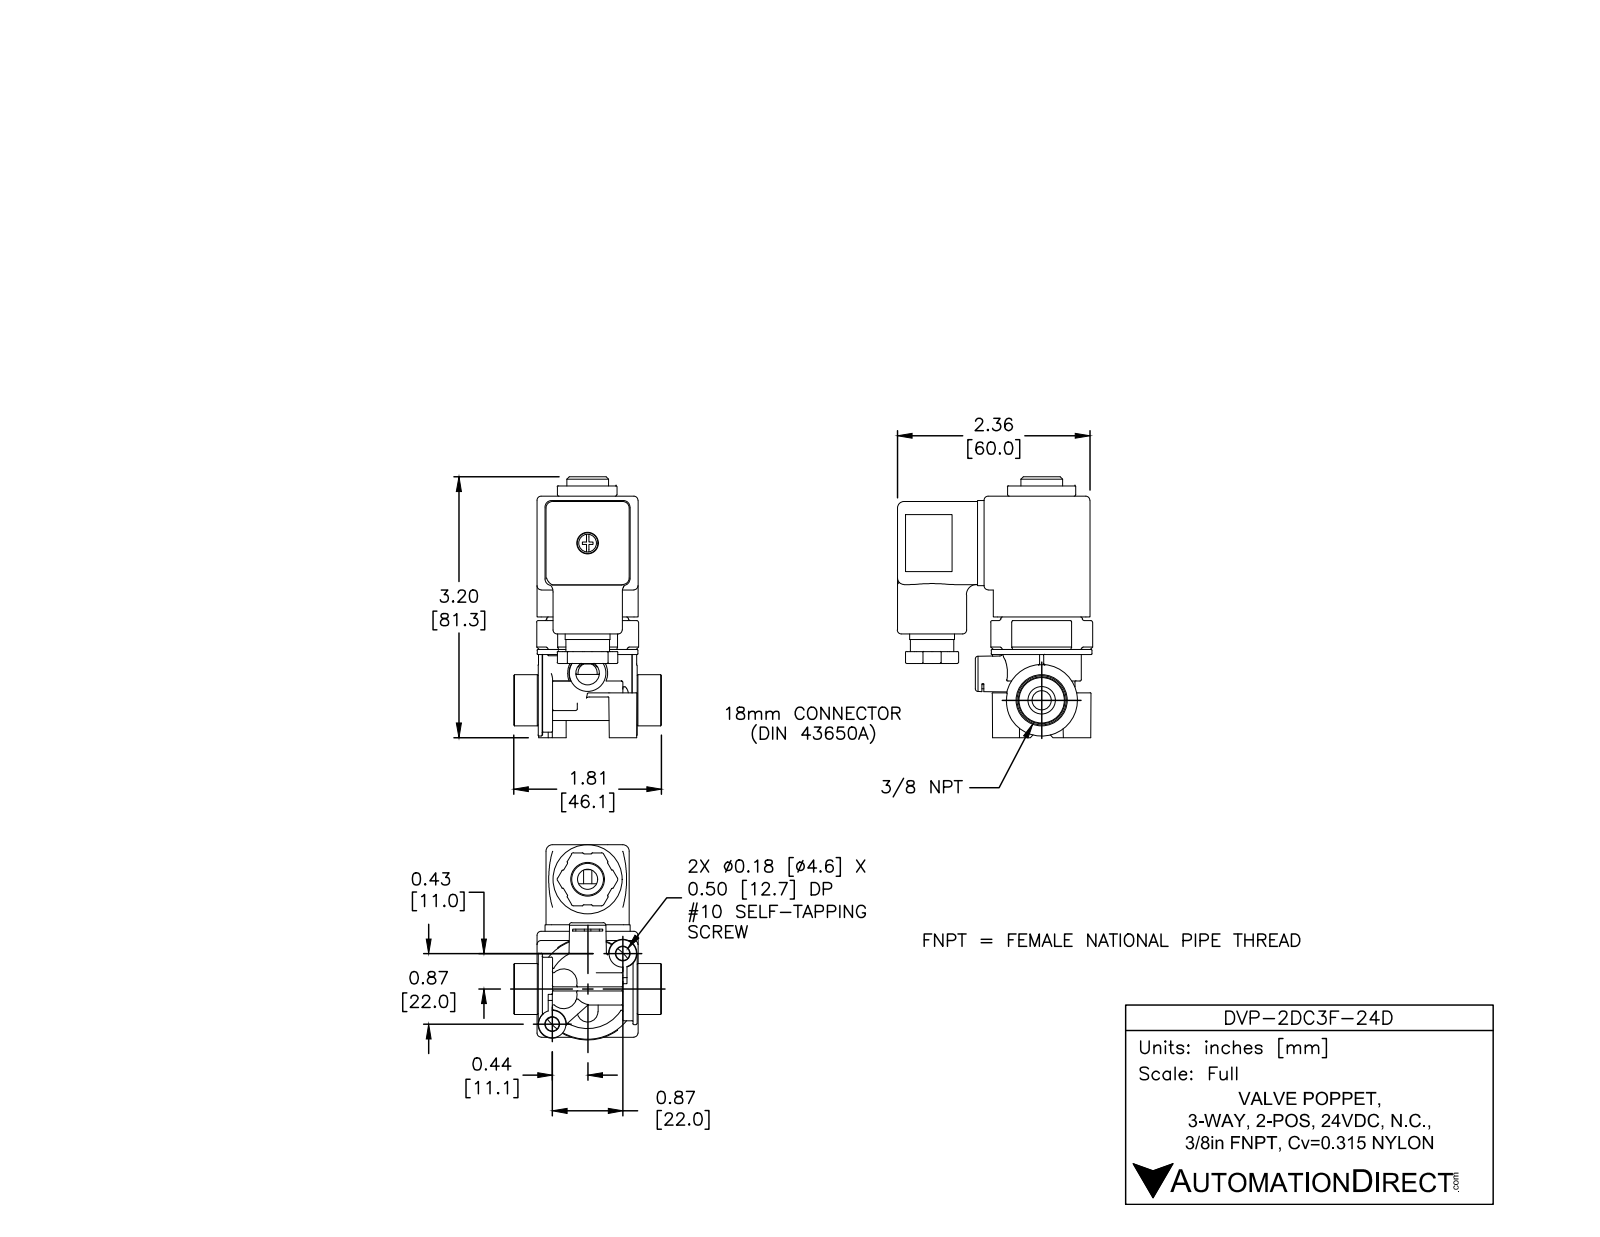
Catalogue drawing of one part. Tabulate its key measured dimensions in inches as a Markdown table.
| quantity | value |
| --- | --- |
| part name | DVP-2DC3F-24D |
| STEP written by | SolidWorks 2015 (AUTOMOTIVE_DESIGN) |
| units | inches |
| bodies | 2 solids, 1760 faces (802 planar, 336 cylindrical, 622 other) |
| overall size | 3.216 × 2.395 × 1.813 |
| volume | 3.958 in³ |
| surface area | 54.46 in² |
| round holes (diameter × count) | 0.06 × 2, 0.236 × 2, 0.095 × 1, 0.102 × 1, 0.12 × 1, 0.203 × 1, 0.245 × 1, 0.25 × 1, 0.263 × 1, 0.287 × 1, 0.37 × 1, 0.39 × 1 |
| round bosses / shafts (diameter × count) | 0.875 × 2, 0.29 × 2, 1.236 × 1, 1 × 1, 0.972 × 1, 0.875 × 1, 0.85 × 1, 0.78 × 1 |
| partial cylindrical surfaces (radius × count) | 0.01 × 74, 0.015 × 34, 0.05 × 21, 0.02 × 12, 0.08 × 12, 0.026 × 6, 0.03 × 6, 0.04 × 4 |
| main face-to-face distances | 1.083, 1.24, 0.048, 0.157, 0.08, 0.925, 1.48, 0.109, 1.131, 0.974 |
| hole center spacings | 0.281, 0.283, 1.062, 1.343, 1.345, 1.612, 1.626, 2.184 |
